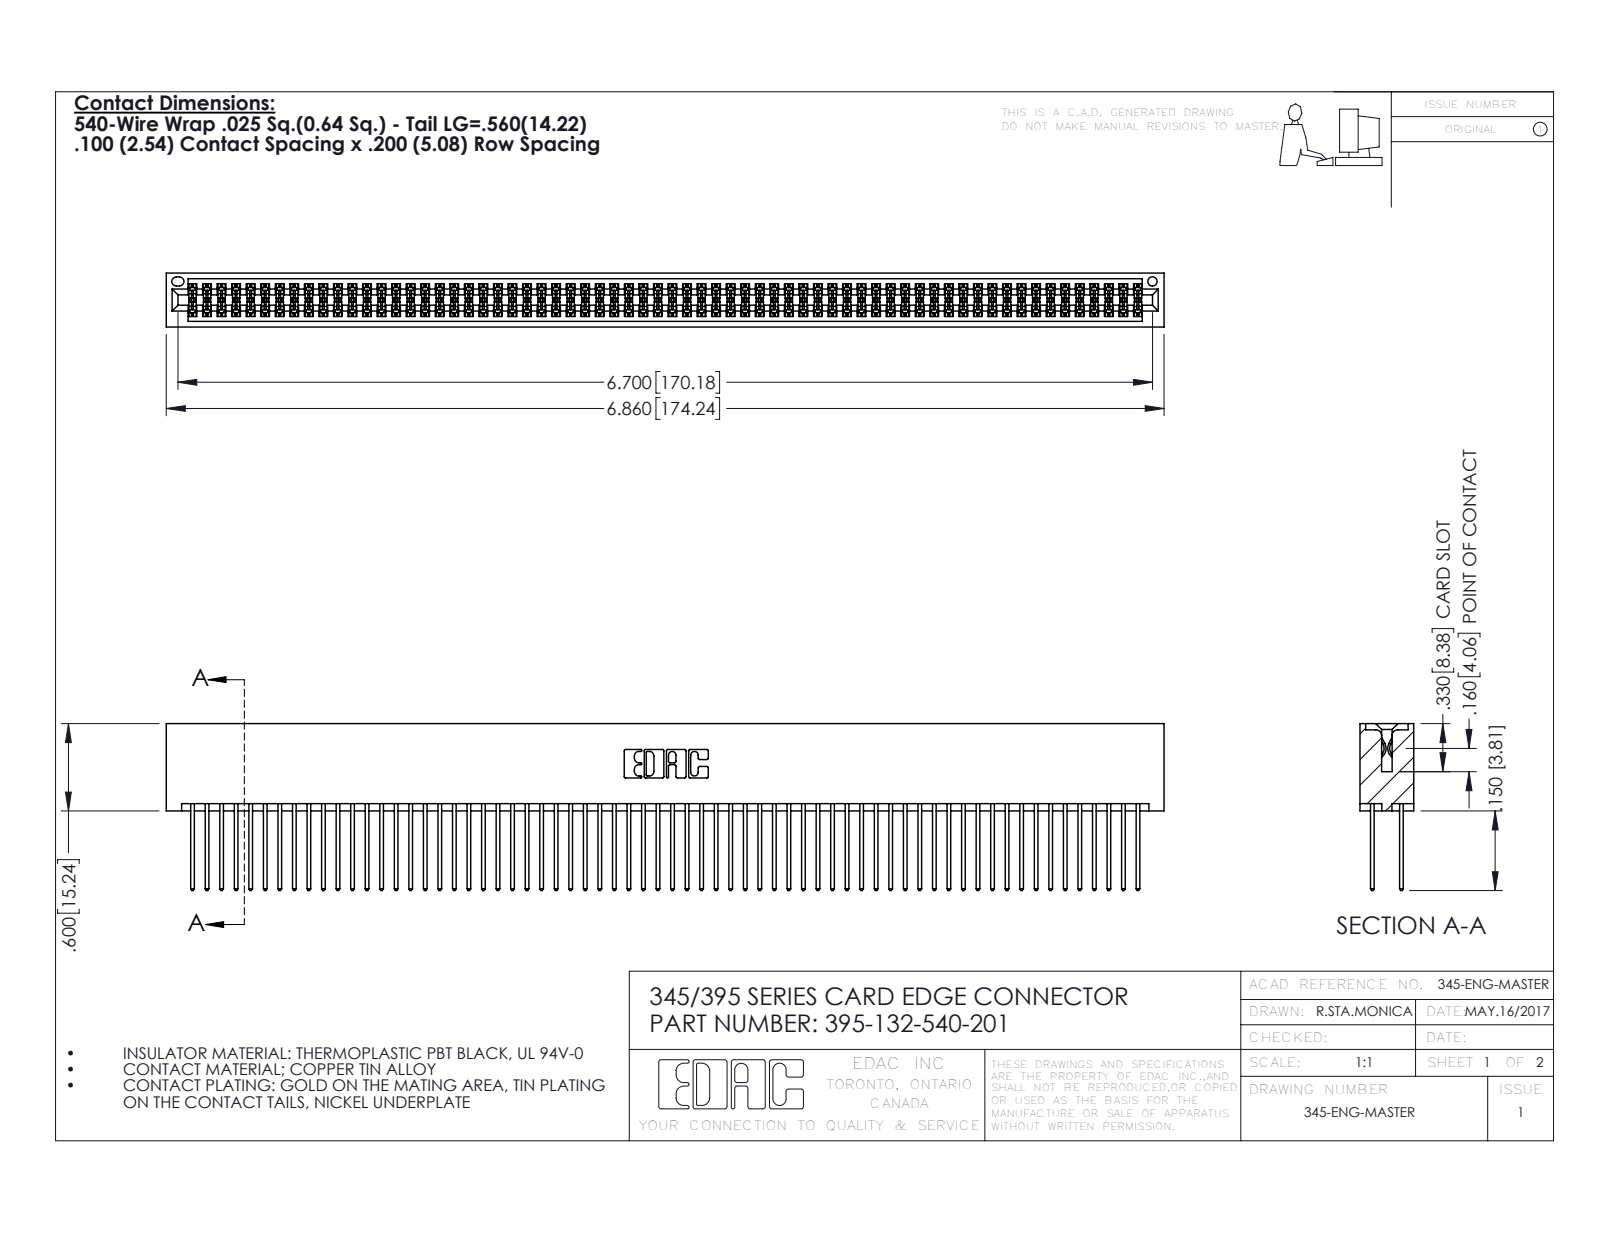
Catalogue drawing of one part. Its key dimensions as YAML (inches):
part_name: "345-292-001_345-293-140; 345 Part_No Mounting Lugs; 395-132-540-201"
step_written_by: "SolidWorks 2016 (CONFIG_CONTROL_DESIGN)"
units: inches
bodies: {solids: 133, faces: 6718, planar: 4432, cylindrical: 2286, other: 0}
overall_size: [6.86, 1.147, 0.37]
volume: 1.115
surface_area: 46.64
round_holes:
  - {diameter: 0.064, count: 1}
partial_cylinders:
  - {radius: 0.006, count: 198}
  - {radius: 0.01, count: 132}
  - {radius: 0.01, count: 22}
  - {radius: 0.007, count: 6}
  - {radius: 0.031, count: 6}
  - {radius: 0.026, count: 3}
  - {radius: 0.014, count: 2}
  - {radius: 0.019, count: 2}
face_to_face_distances: [0.298, 0.072, 0.2, 0.098, 0.272, 0.025, 0.225, 0.37, 0.175, 0.149]
